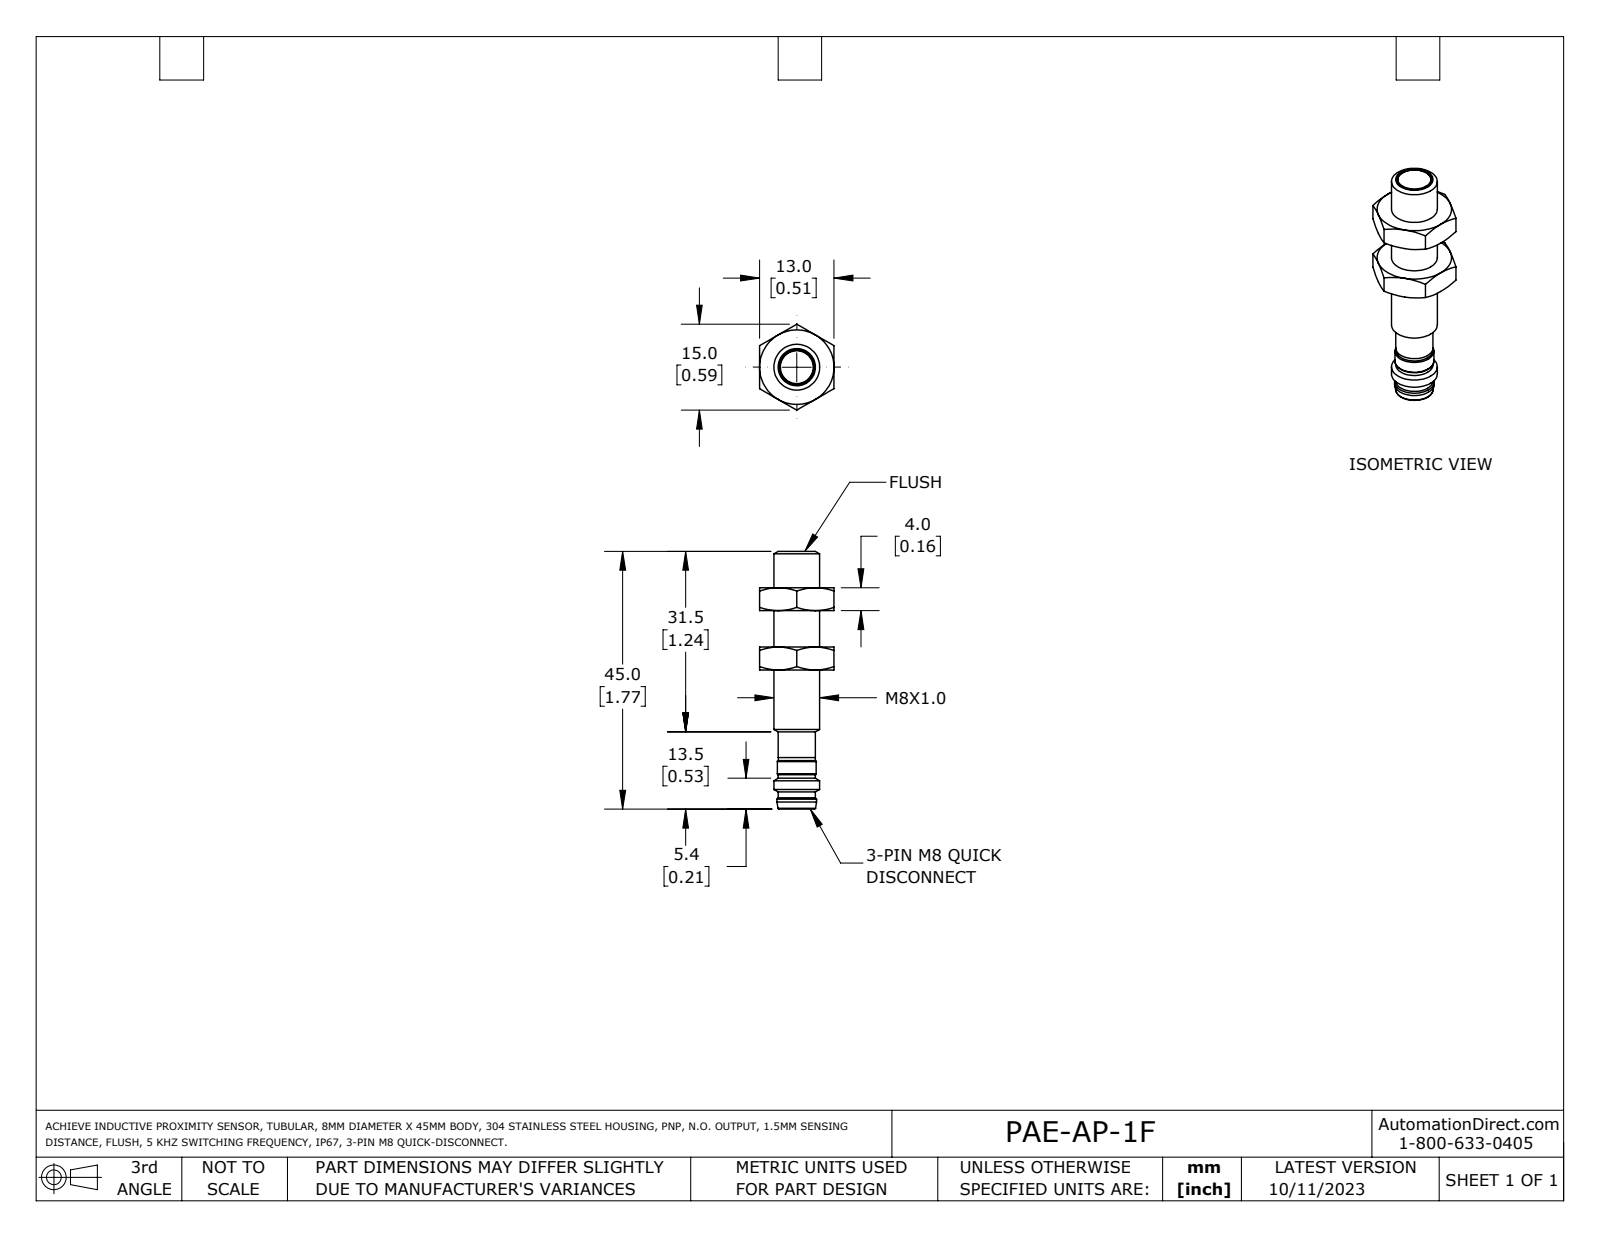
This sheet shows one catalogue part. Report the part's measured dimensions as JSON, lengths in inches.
{"part_name": "PAE-AP-1F", "step_written_by": "SolidWorks 2023 (AUTOMOTIVE_DESIGN)", "units": "inches", "bodies": {"solids": 3, "faces": 77, "planar": 27, "cylindrical": 14, "other": 36}, "overall_size": [1.772, 0.591, 0.512], "volume_in3": 0.165, "surface_area_in2": 3.471, "round_holes": [[0.228, 1], [0.315, 1]], "round_bosses_or_shafts": [[0.039, 3], [0.272, 1], [0.268, 1], [0.256, 1], [0.254, 1]], "face_to_face_distances": [0.407, 0.157, 0.512, 0.25, 0.565, 0.815, 0.657, 0.917, 1.325, 0.76]}
